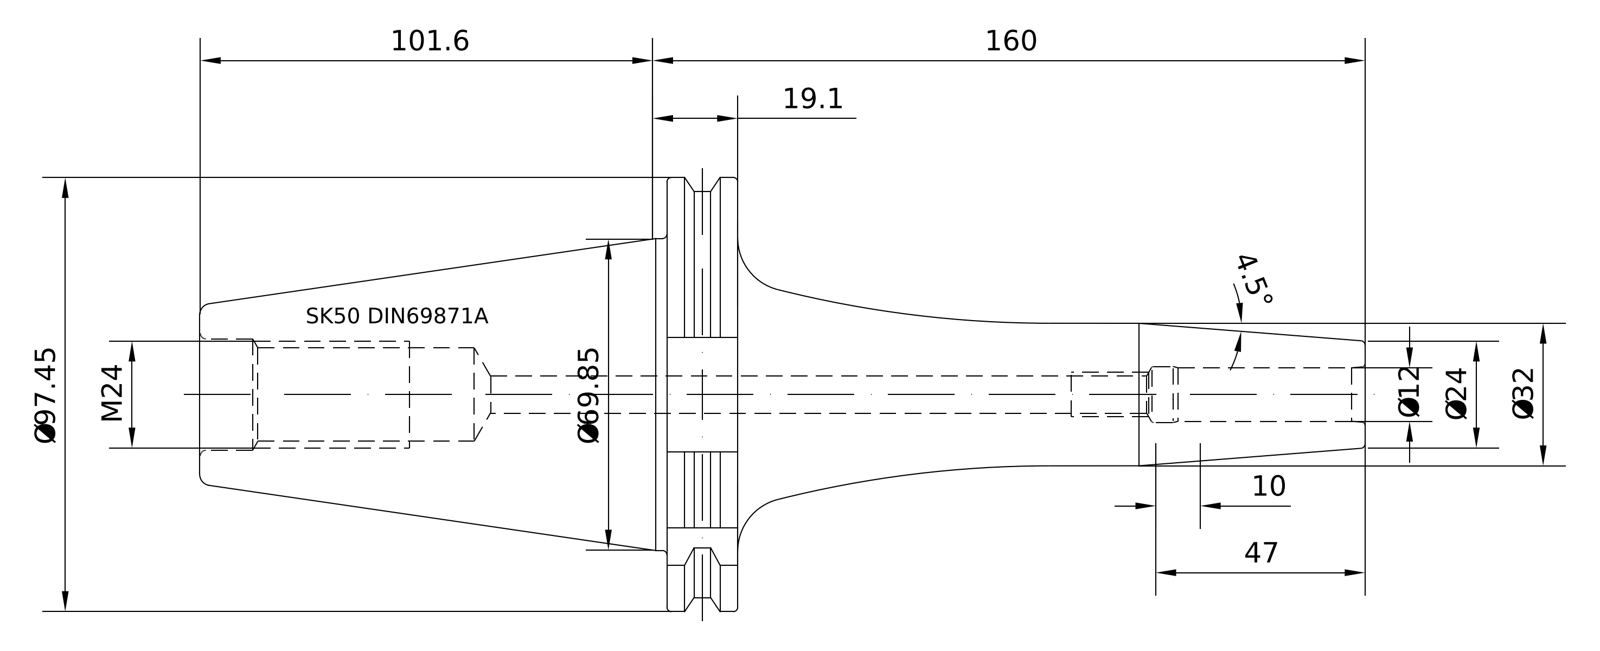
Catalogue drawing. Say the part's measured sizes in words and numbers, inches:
The part is named "50-442-12". Its 3-D file was written by "PRO/ENGINEER BY PARAMETRIC TECHNOLOGY CORPORATION, 2010430 (CONFIG_CONTROL_DESIGN)". It is 1 solid with 95 faces: 21 planar, 24 cylindrical and 50 other. Overall it measures 10.299 by 3.837 by 3.701 inches. Its volume is 28.59 cubic inches and its surface area 89.05 square inches. Round holes: 1 of diameter 0.472, 1 of diameter 0.817, 1 of diameter 0.985, 1 of diameter 1.012. Round bosses or shafts: 1 of diameter 3.583, 1 of diameter 2.722, 1 of diameter 1.26, 1 of diameter 0.945. Partial cylindrical surfaces (rounded edges, fillets, slot ends): 1 of radius 0.069, 1 of radius 1.919. The main face-to-face distances are 0.624, 2.866, 4.126, 4.75, 1.016, 10.299, 6.173, 5.549, 1.89, 2.236.
